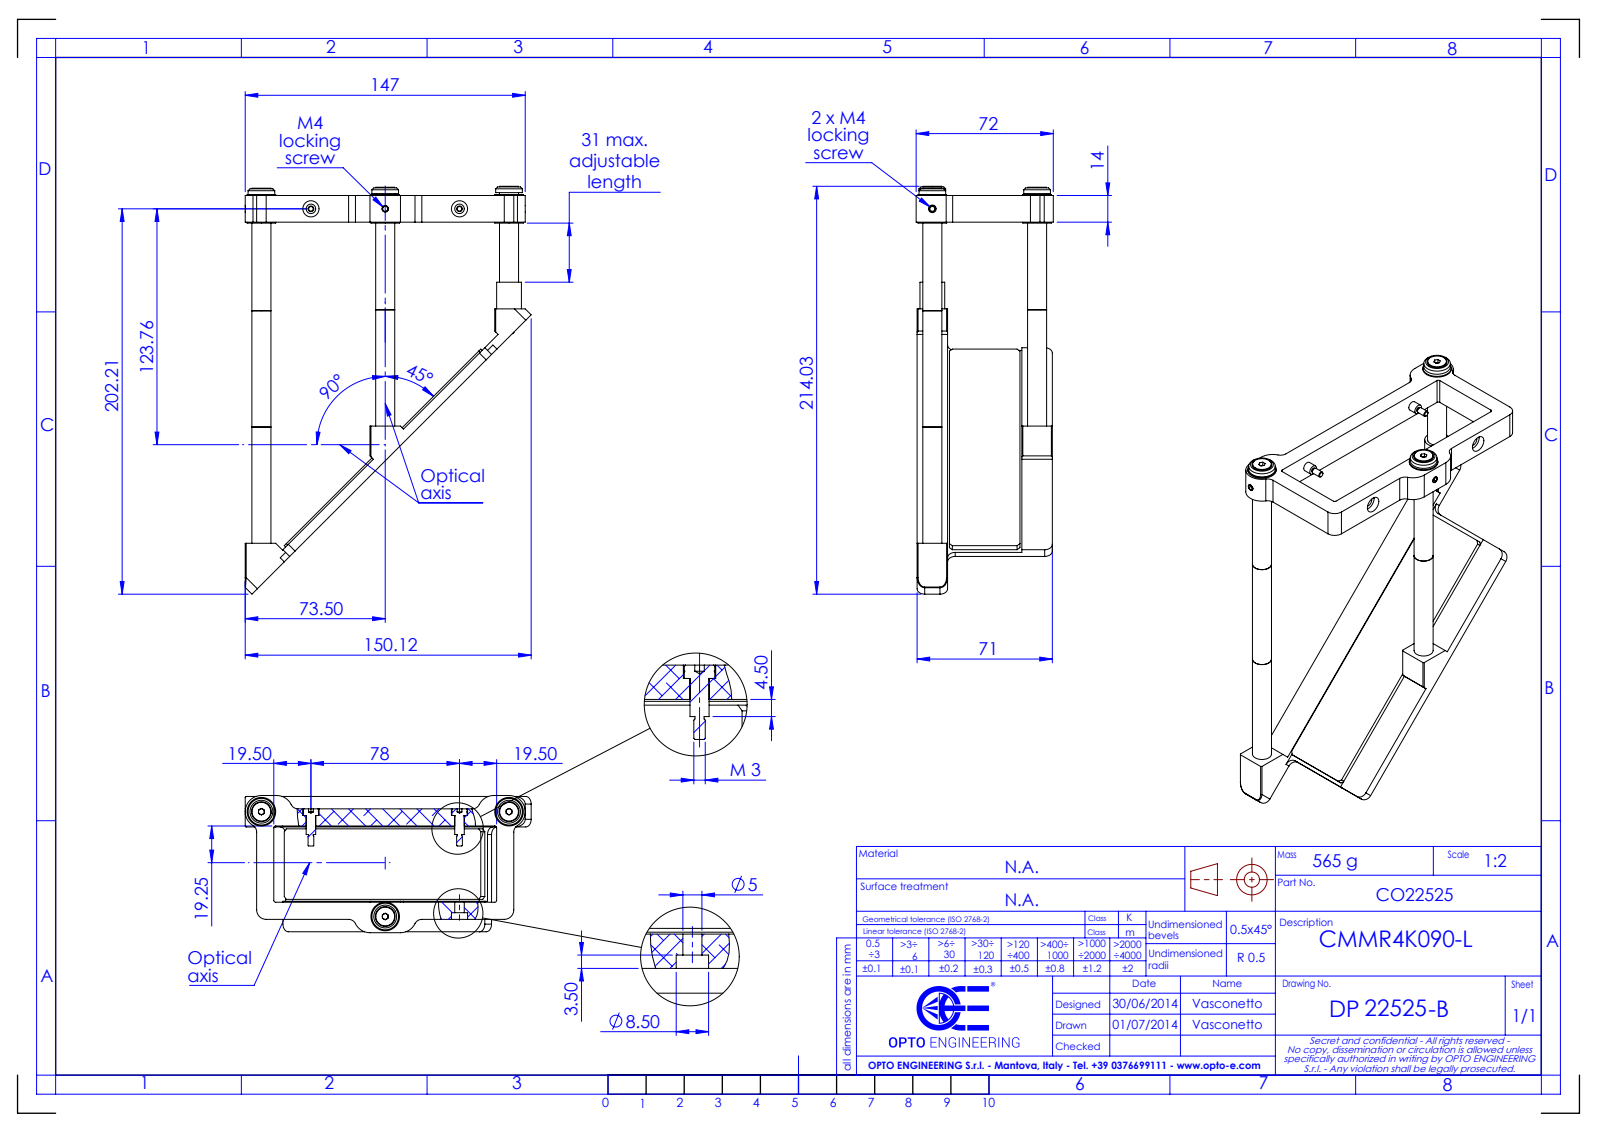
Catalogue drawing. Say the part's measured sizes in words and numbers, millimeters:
The part is named "DP22525-B_CMMR4K090-L". Its 3-D file was written by "SolidWorks 2021 (CONFIG_CONTROL_DESIGN)". It is 0 solids with 268 faces: 134 planar, 98 cylindrical and 36 other. Overall it measures 214.03 by 150.12 by 72 millimeters. Round holes: 3 of diameter 4.2, 2 of diameter 5, 2 of diameter 8.5. Round bosses or shafts: 3 of diameter 15, 3 of diameter 14, 3 of diameter 10, 3 of diameter 9.85, 2 of diameter 3, 2 of diameter 2.39, 1 of diameter 13, 1 of diameter 8. Partial cylindrical surfaces (rounded edges, fillets, slot ends): 14 of radius 4, 6 of radius 8.5, 4 of radius 1, 2 of radius 5. The main face-to-face distances are 3, 6, 1, 2, 5, 14, 9, 55.5, 0.5, 49. The hole center spacings are 85.15, 78, 130.
